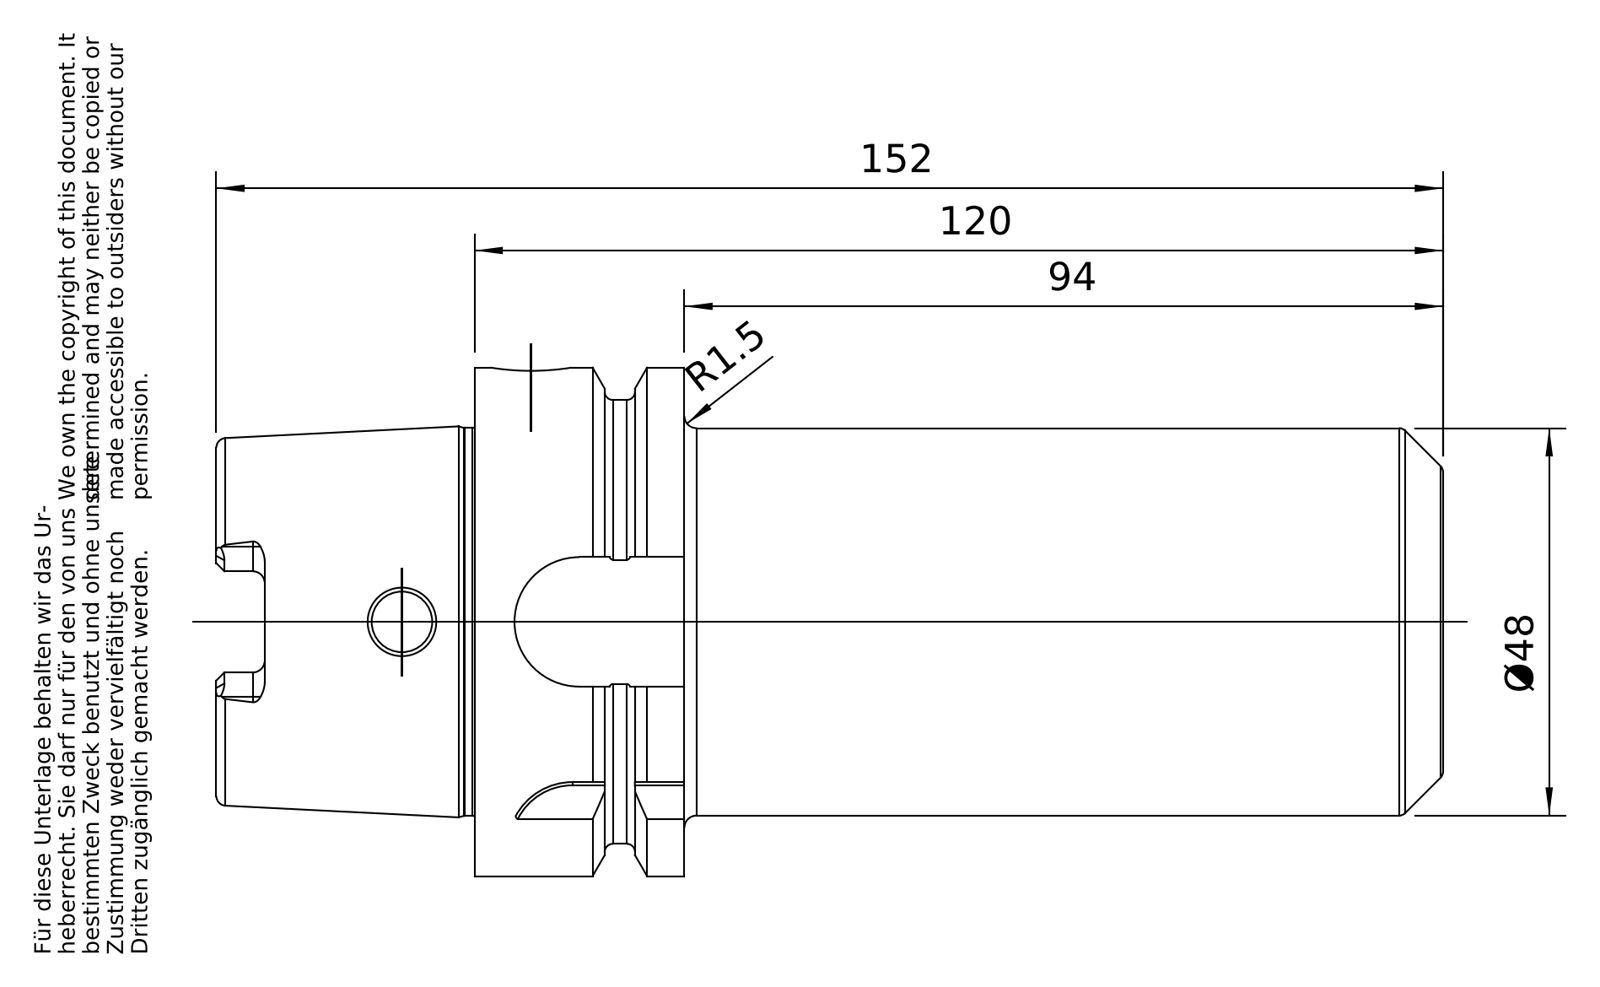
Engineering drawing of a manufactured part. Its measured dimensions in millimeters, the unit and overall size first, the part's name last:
Units: millimetres
Overall size (bounding box): 152 × 63 × 63
Round holes (diameter × count): ⌀7.5 ×1, ⌀10 ×1, ⌀16.92 ×1, ⌀18.32 ×1, ⌀18.66 ×1, ⌀24.72 ×1, ⌀34 ×1, ⌀40 ×1
Round bosses / shafts (diameter × count): ⌀63 ×1, ⌀55 ×1, ⌀48.04 ×1, ⌀48 ×1, ⌀18 ×1
Partial cylindrical surfaces — rounded edges, fillets, slot ends (radius × count): R1.5 ×6, R3 ×4, R8 ×1, R8.02 ×1, R9.02 ×1
Main face-to-face distances: 26, 10, 120, 94, 16, 110, 47.3, 37.3, 21.3, 72.7
Volume: 214 061 mm³ · Surface area: 41 848 mm²
Bodies: 1 solid, 177 faces (57 planar, 48 cylindrical, 72 other)
Part name (STEP PRODUCT): A63-120-03
STEP written by: PRO/ENGINEER BY PARAMETRIC TECHNOLOGY CORPORATION, 2010430 (CONFIG_CONTROL_DESIGN)
